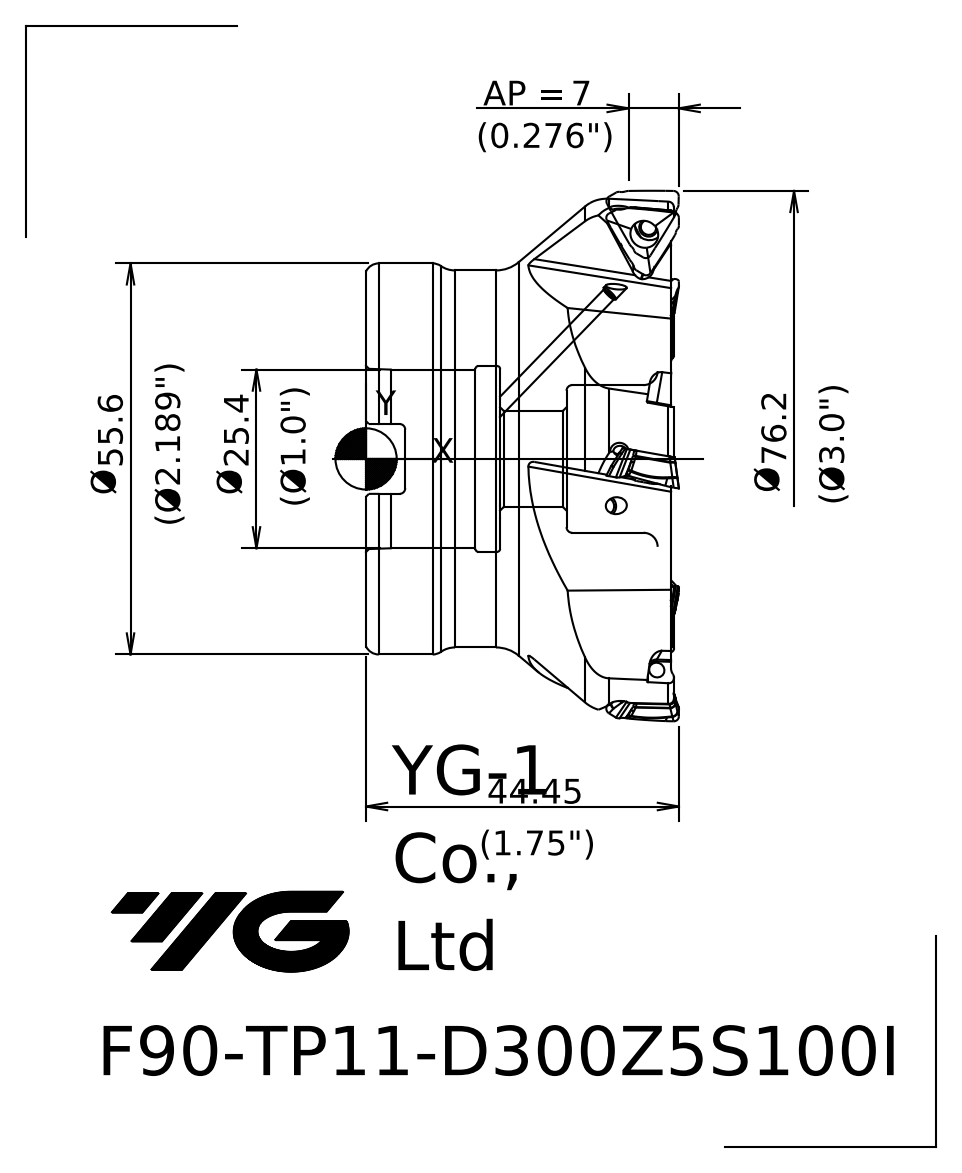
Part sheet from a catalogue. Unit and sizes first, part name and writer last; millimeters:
Units: millimetres
Overall size (bounding box): 76.25 × 76.25 × 44.45
Round holes (diameter × count): ⌀13.7 ×1, ⌀21 ×1, ⌀25.4 ×1, ⌀26.4 ×1
Round bosses / shafts (diameter × count): ⌀55.6 ×1, ⌀53.6 ×1
Partial cylindrical surfaces — rounded edges, fillets, slot ends (radius × count): R0.8 ×2
Main face-to-face distances: 43.35, 1.9, 41.45, 24.3, 22.4, 19.05, 37.79, 35.89, 13.49, 5.56
Volume: 112 924 mm³ · Surface area: 25 191 mm²
Bodies: 1 solid, 76 faces (18 planar, 10 cylindrical, 48 other)
Part name (STEP PRODUCT): 1022B364674Env44
STEP written by: SIEMENS PLM Software NX 10.0 (AP203_CONFIGURATION_CONTROLLED_3D_DESIGN_OF_MECHANICAL_PARTS_AND_ASSEMBLIES_MIM_LF)
